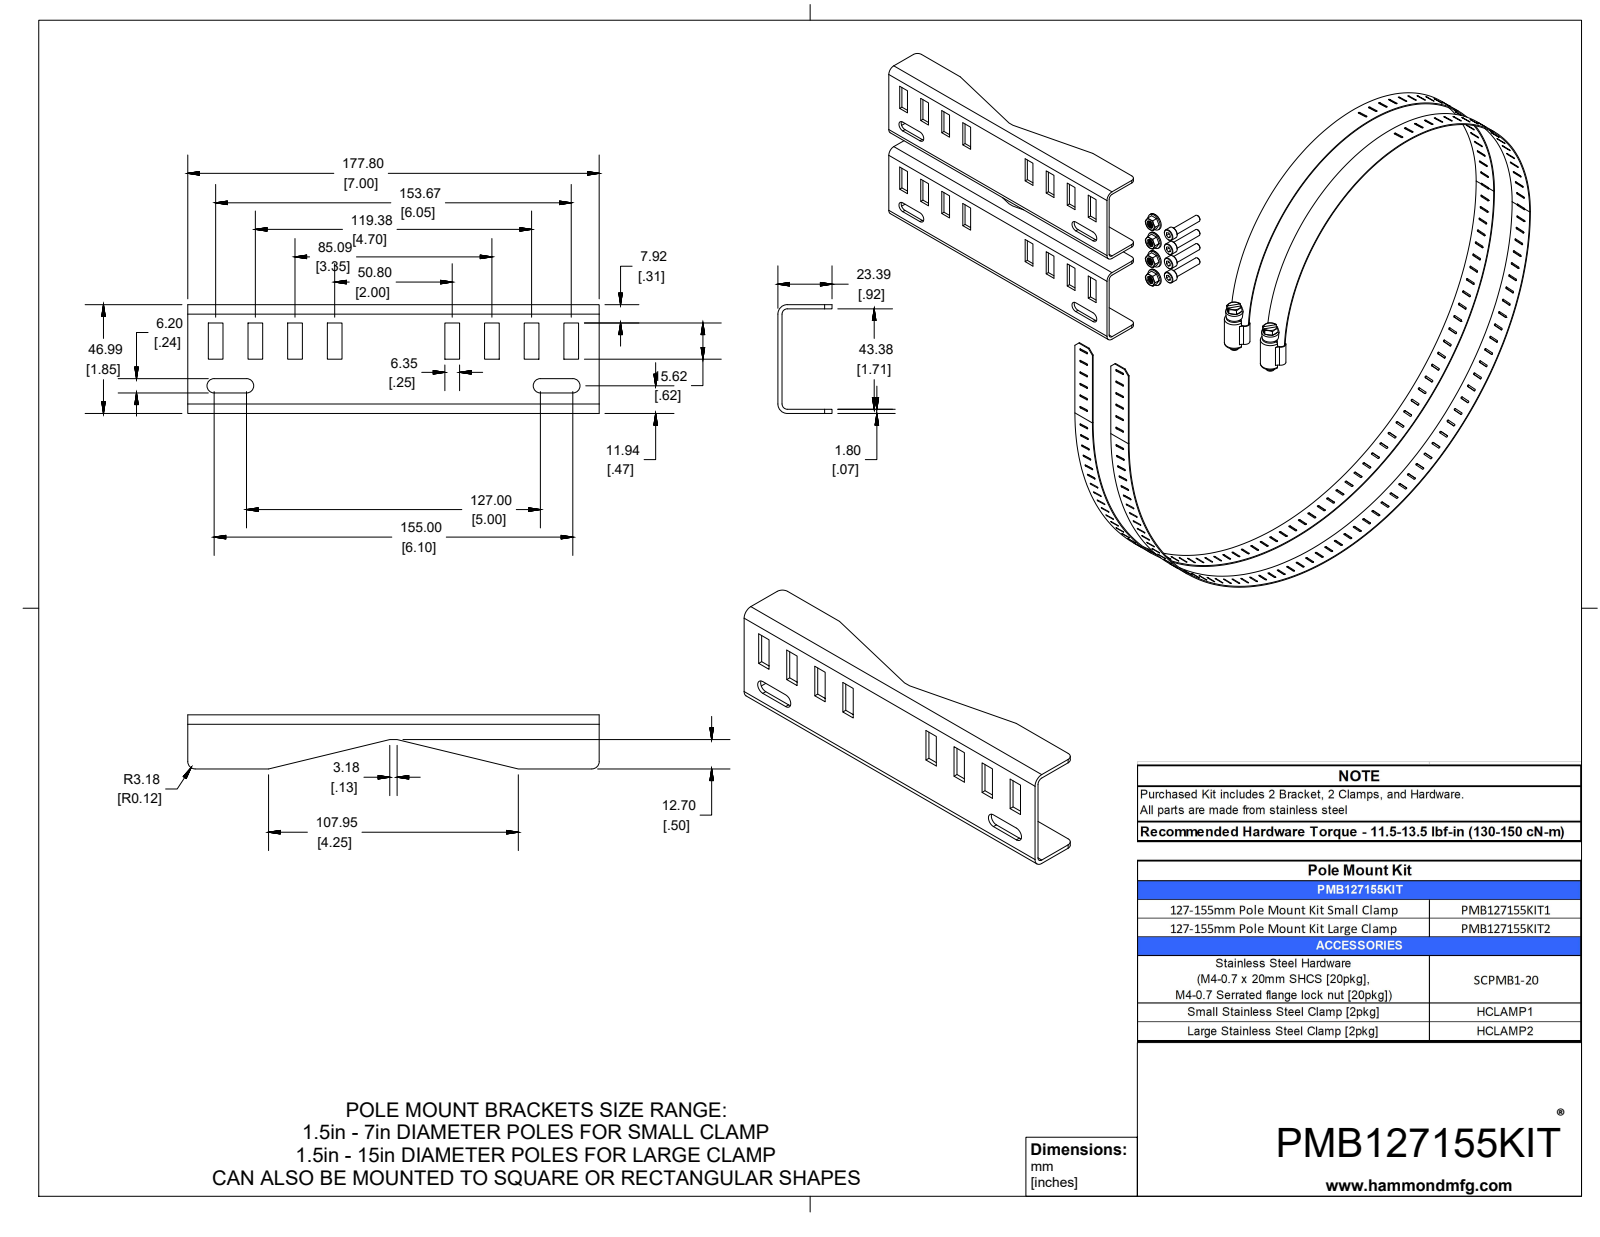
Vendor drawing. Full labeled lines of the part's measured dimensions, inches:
Part name (STEP PRODUCT): PMB127155KIT1
STEP written by: SolidWorks 2019 (CONFIG_CONTROL_DESIGN)
Units: inches
Bodies: 1 solid, 66 faces (54 planar, 12 cylindrical, 0 other)
Overall size (bounding box): 7 × 1.85 × 0.921
Volume: 1.441 in³ · Surface area: 43.34 in²
Partial cylindrical surfaces — rounded edges, fillets, slot ends (radius × count): R0.122 ×4, R0.09 ×2, R0.125 ×2, R0.161 ×2
Main face-to-face distances: 0.071, 1.779, 1.85, 1.708, 0.85, 0.921, 0.25, 0.675, 3.35, 7
